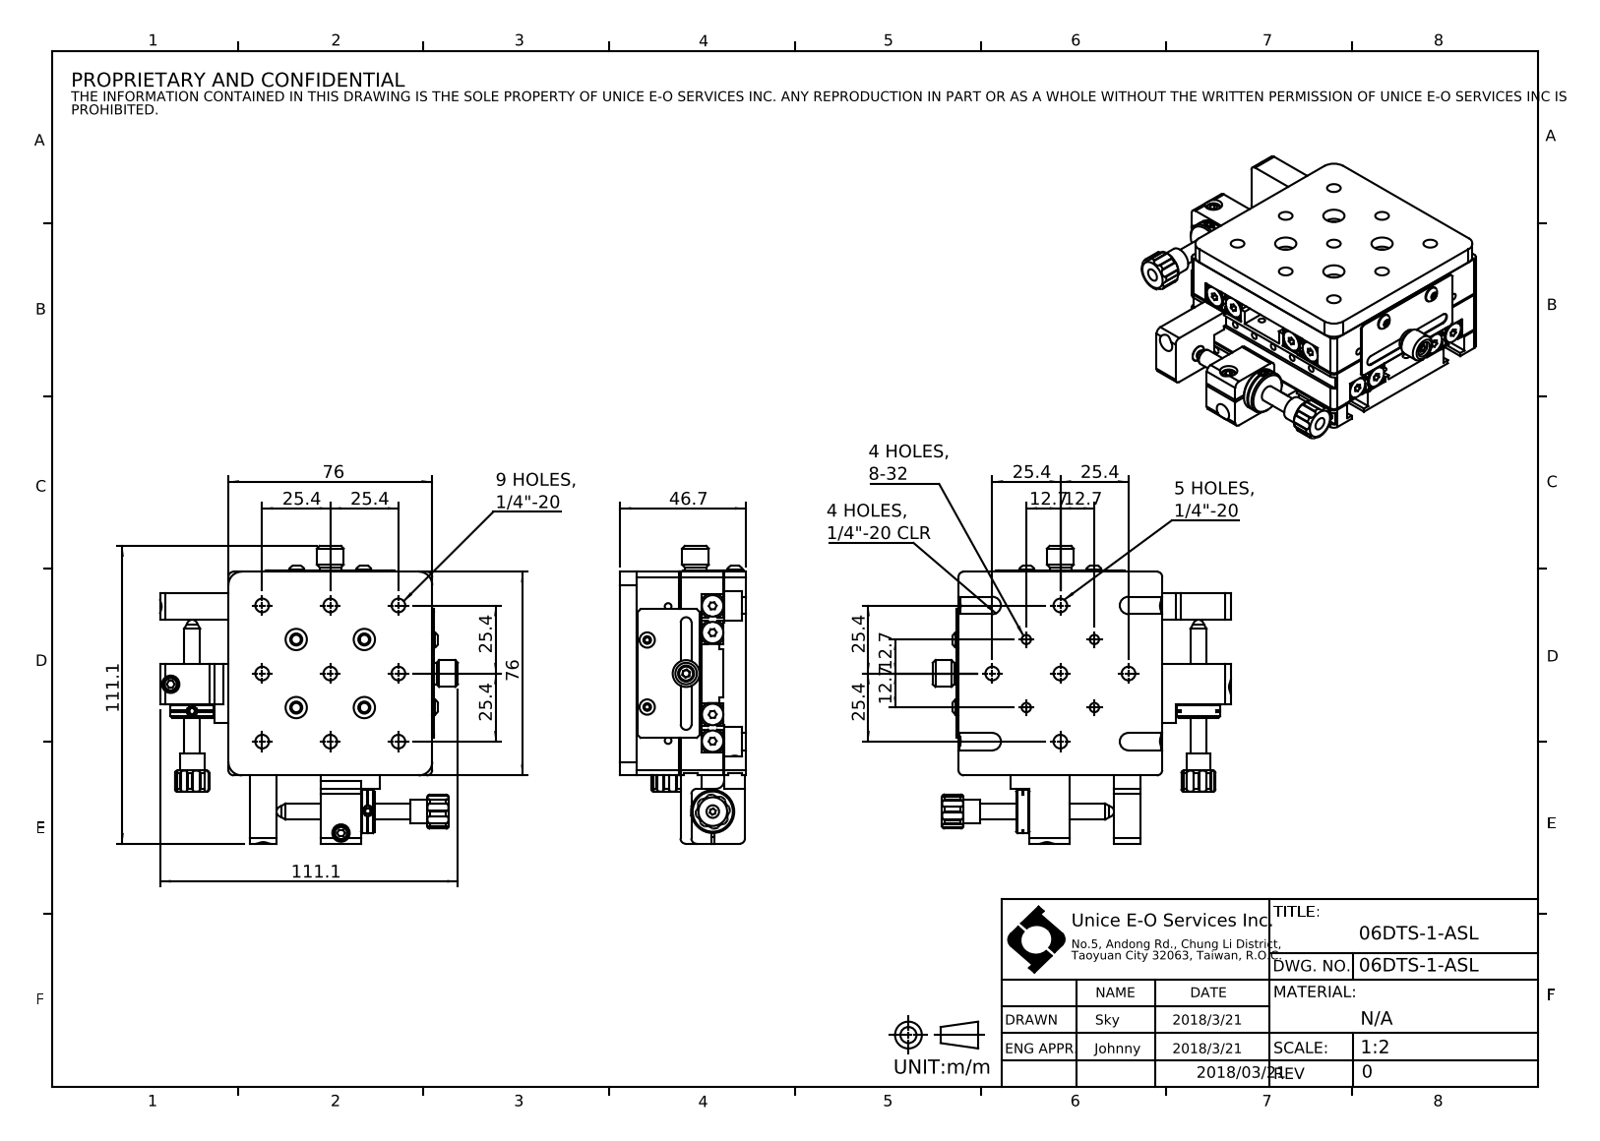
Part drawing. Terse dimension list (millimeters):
name: 06DTS-1-ASL
written by: SolidWorks 2016 (AUTOMOTIVE_DESIGN)
unit: mm
bodies: 0 solids, 974 faces (499 planar, 335 cylindrical, 140 other)
size: 111.1 × 111.1 × 46.7
holes: 34× ⌀2.5, 9× ⌀5.11, 8× ⌀6.5, 4× ⌀3.45, 4× ⌀4.5, 4× ⌀7.94, 2× ⌀4.7, 2× ⌀6, 2× ⌀10
bosses: 10× ⌀8, 4× ⌀5.7, 2× ⌀16, 2× ⌀10, 2× ⌀9, 2× ⌀6, 2× ⌀4
rounds: 32× R0.3, 20× R2, 16× R2.75, 4× R3.25, 4× R5, 4× R5.5, 2× R3, 2× R6.35
face distances: 16.4, 8.5, 16.1, 7.9, 8.3, 8.2, 24.6, 24.3, 8, 6
hole spacings: 10, 20, 17.96, 25.4, 40.16, 30, 19.25, 19.17
